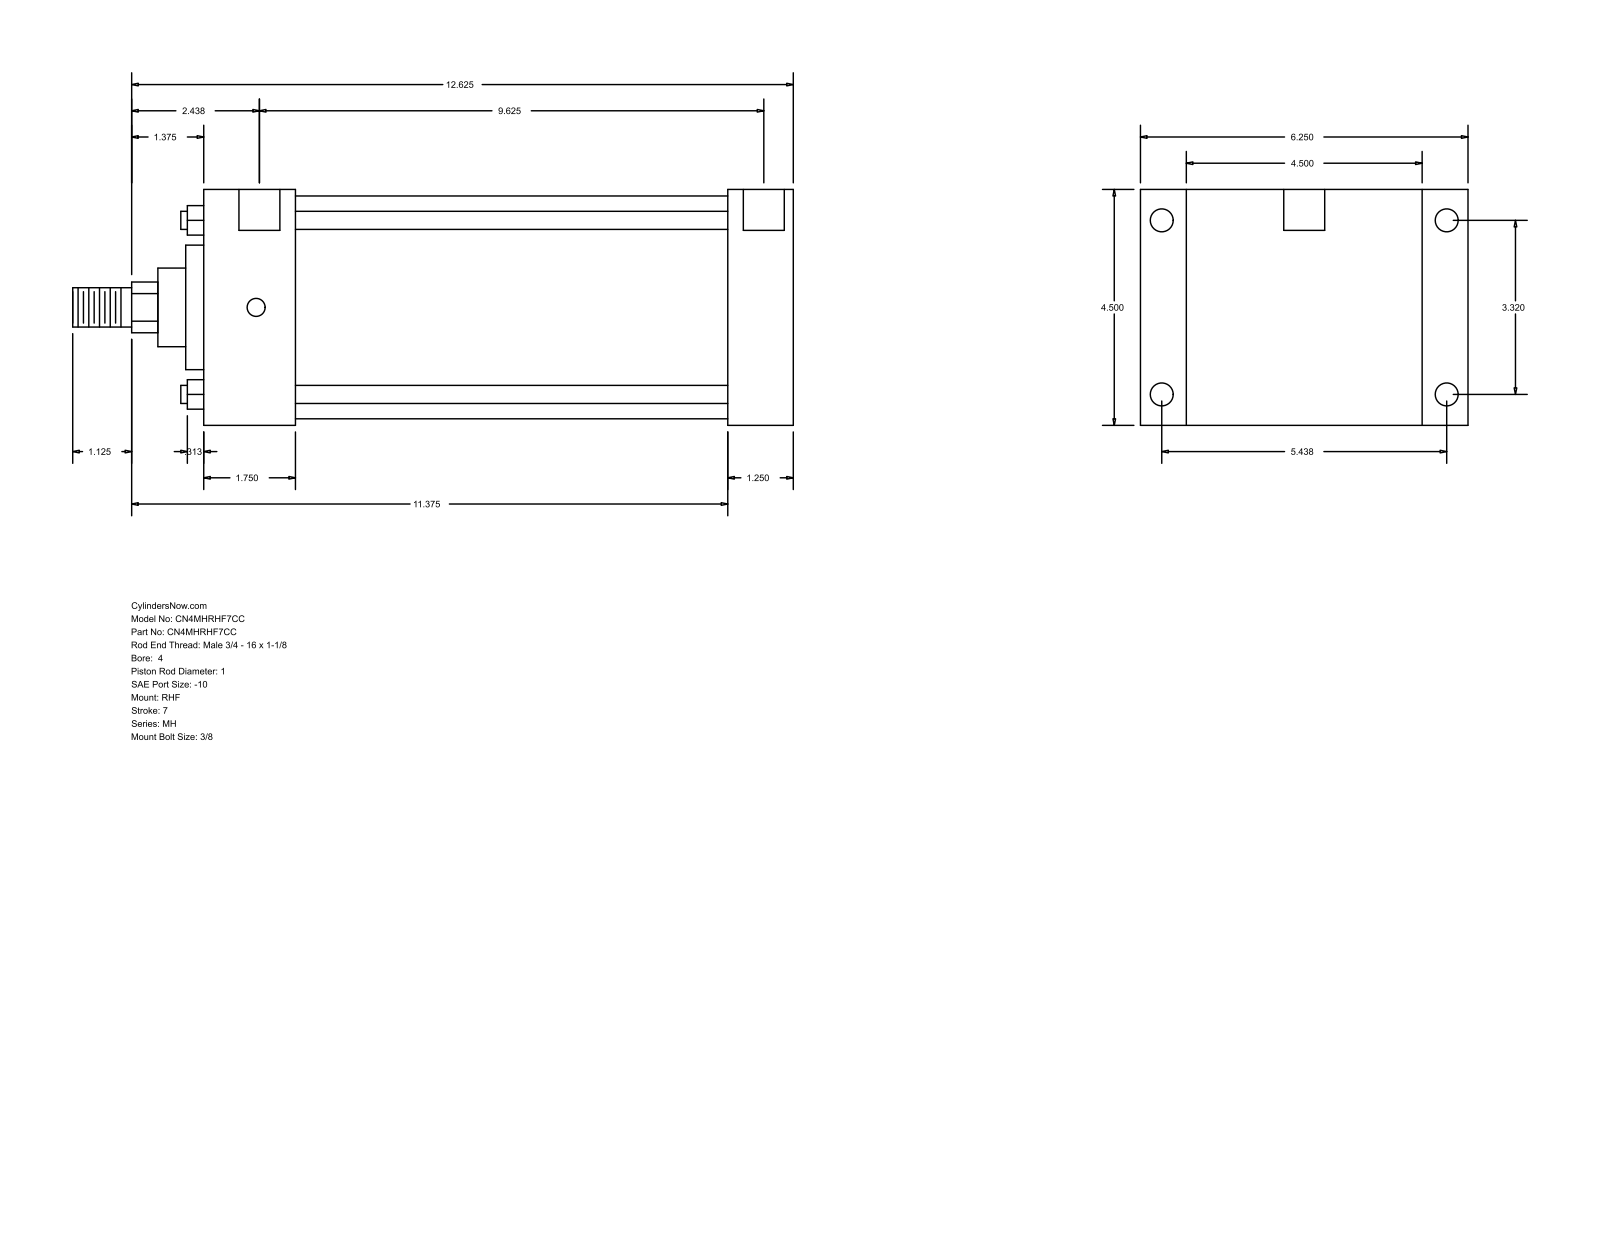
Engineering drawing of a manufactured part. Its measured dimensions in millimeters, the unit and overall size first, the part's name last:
Units: millimetres
Overall size (bounding box): 349.25 × 158.75 × 114.3
Round holes (diameter × count): ⌀8.73 ×4, ⌀11.13 ×4, ⌀19.84 ×2
Round bosses / shafts (diameter × count): ⌀8.76 ×4, ⌀107.95 ×1, ⌀60.33 ×1, ⌀38.1 ×1, ⌀25.4 ×1, ⌀19.05 ×1
Partial cylindrical surfaces — rounded edges, fillets, slot ends (radius × count): R12.29 ×1
Main face-to-face distances: 114.3, 285.76, 254.01, 31.75, 22.23, 136.53, 44.46, 209.55, 241.3, 158.76
Hole centre spacings: 84.32, 138.12, 161.82, 247.65, 1.58, 1.59, 244.48, 246.06
Bodies: 0 solids, 90 faces (61 planar, 29 cylindrical, 0 other)
Part name (STEP PRODUCT): MH_RHF__0400_1
STEP written by: GSSL Pune (CONFIG_CONTROL_DESIGN)
